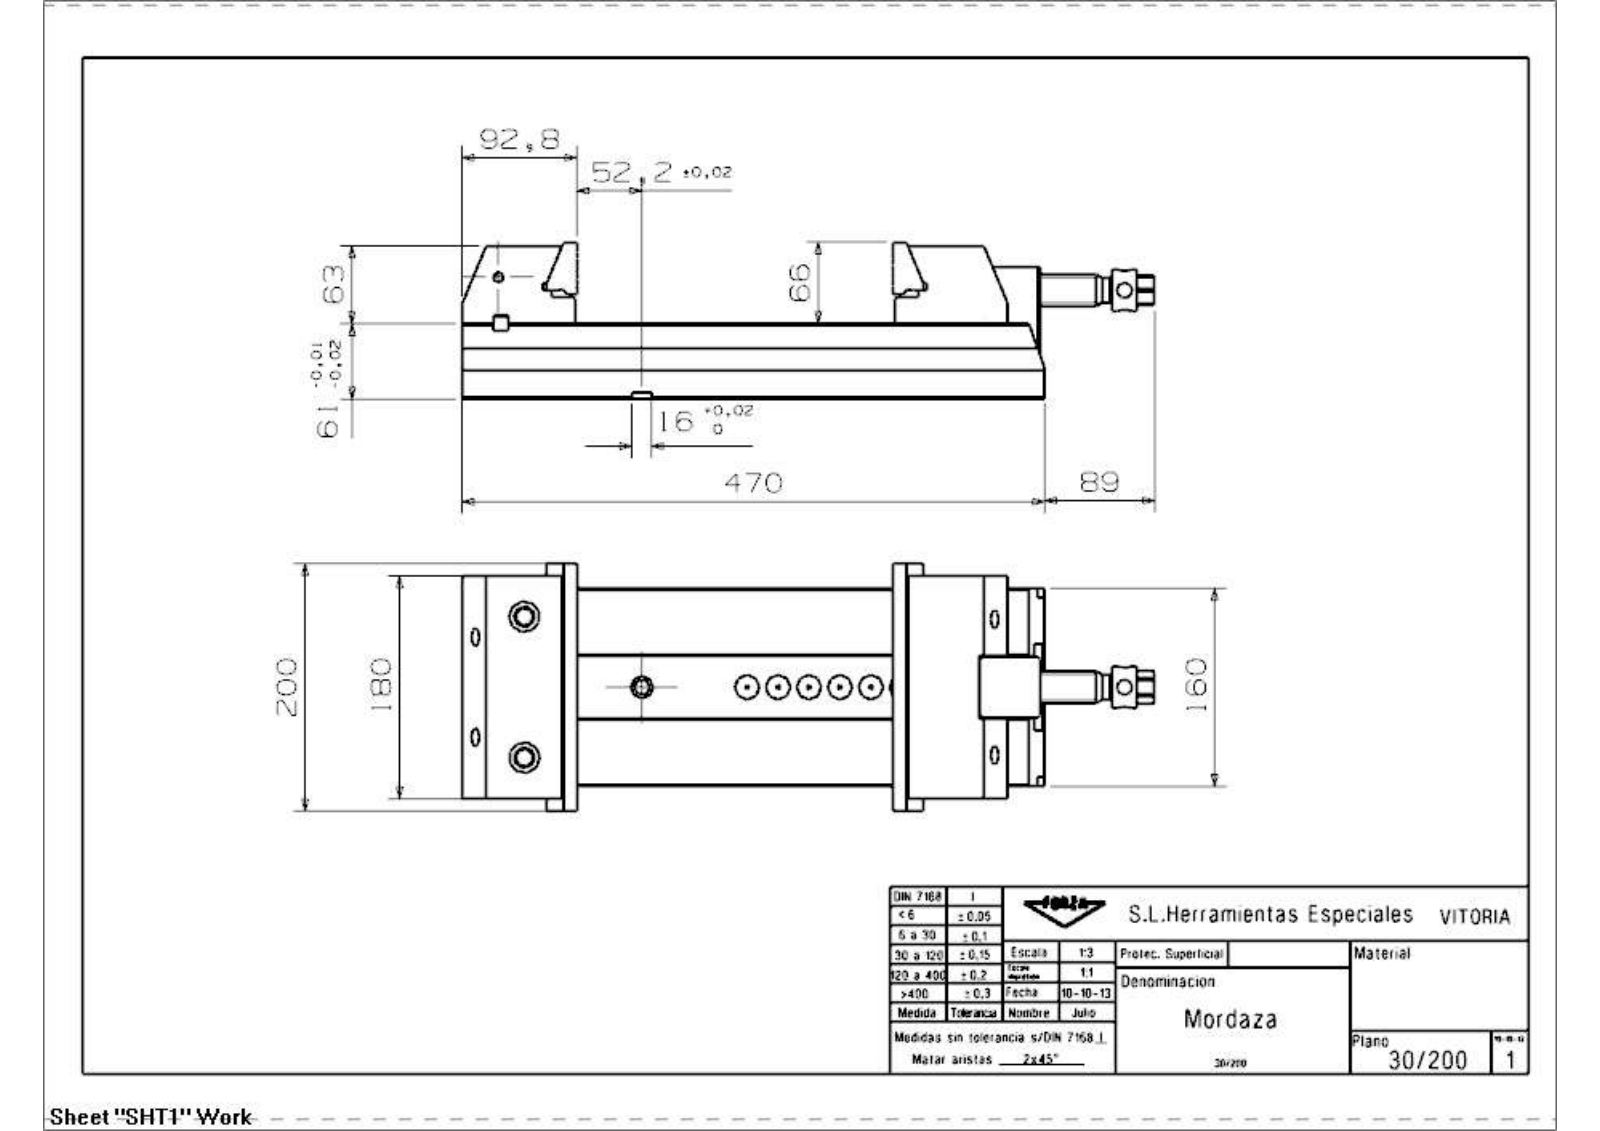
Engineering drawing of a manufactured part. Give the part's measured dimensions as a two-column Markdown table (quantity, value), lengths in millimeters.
| quantity | value |
| --- | --- |
| part name | 30_200_Mordaza |
| STEP written by | SIEMENS PLM Software NX 7.5 (CONFIG_CONTROL_DESIGN) |
| units | millimeters |
| bodies | 12 solids, 483 faces (288 planar, 132 cylindrical, 63 other) |
| overall size | 559 × 200 × 126.95 |
| volume | 5 534 000 mm³ |
| surface area | 591 512 mm² |
| round holes (diameter × count) | 15 × 6, 5.19 × 5, 13 × 5, 6.99 × 4, 8.5 × 4, 10 × 4, 8.78 × 3, 10.58 × 3, 19 × 3, 12 × 2, 12.38 × 2, 14.38 × 2 |
| round bosses / shafts (diameter × count) | 34 × 1, 33.8 × 1, 26 × 1, 20 × 1, 16.5 × 1 |
| partial cylindrical surfaces (radius × count) | 0.4 × 24, 8 × 4, 20 × 4, 1.6 × 2, 6 × 2, 7 × 2, 4 × 1, 9 × 1 |
| main face-to-face distances | 61, 29.2, 31.8, 124, 94.8, 63, 10, 45, 160, 55 |
| hole center spacings | 14.5, 95.5, 81, 110, 16.47, 16.55, 24.52, 30 |
